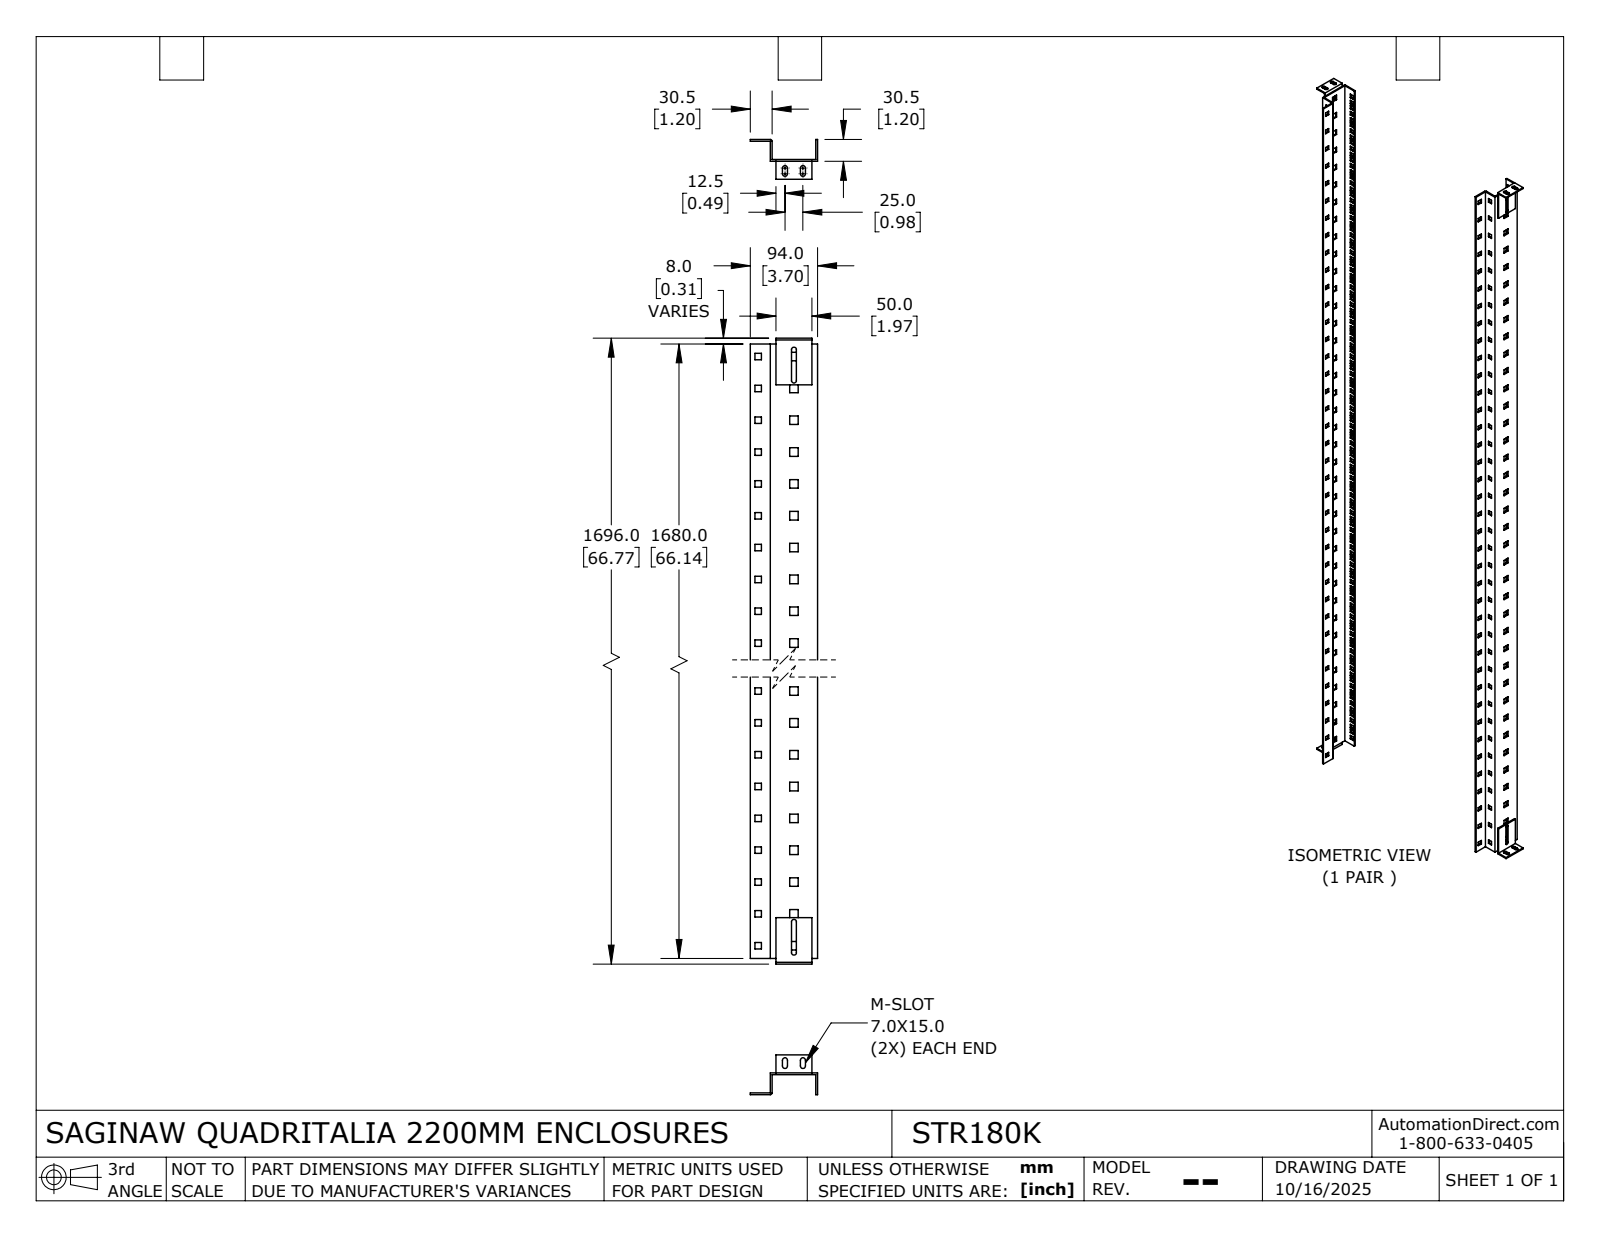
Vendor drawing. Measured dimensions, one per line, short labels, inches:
name: STR180K
written by: SolidWorks 2024 (AUTOMOTIVE_DESIGN)
unit: in
bodies: 6 solids, 1914 faces (1888 planar, 26 cylindrical, 0 other)
size: 66.772 × 22.087 × 3.701
volume: 72.65 in³; area: 1 578 in²
rounds: 12× R0.138, 2× R0.099
face distances: 0.098, 1.102, 20.02, 18.917, 2.5, 20.118, 1.201, 19.016, 19.921, 18.819
